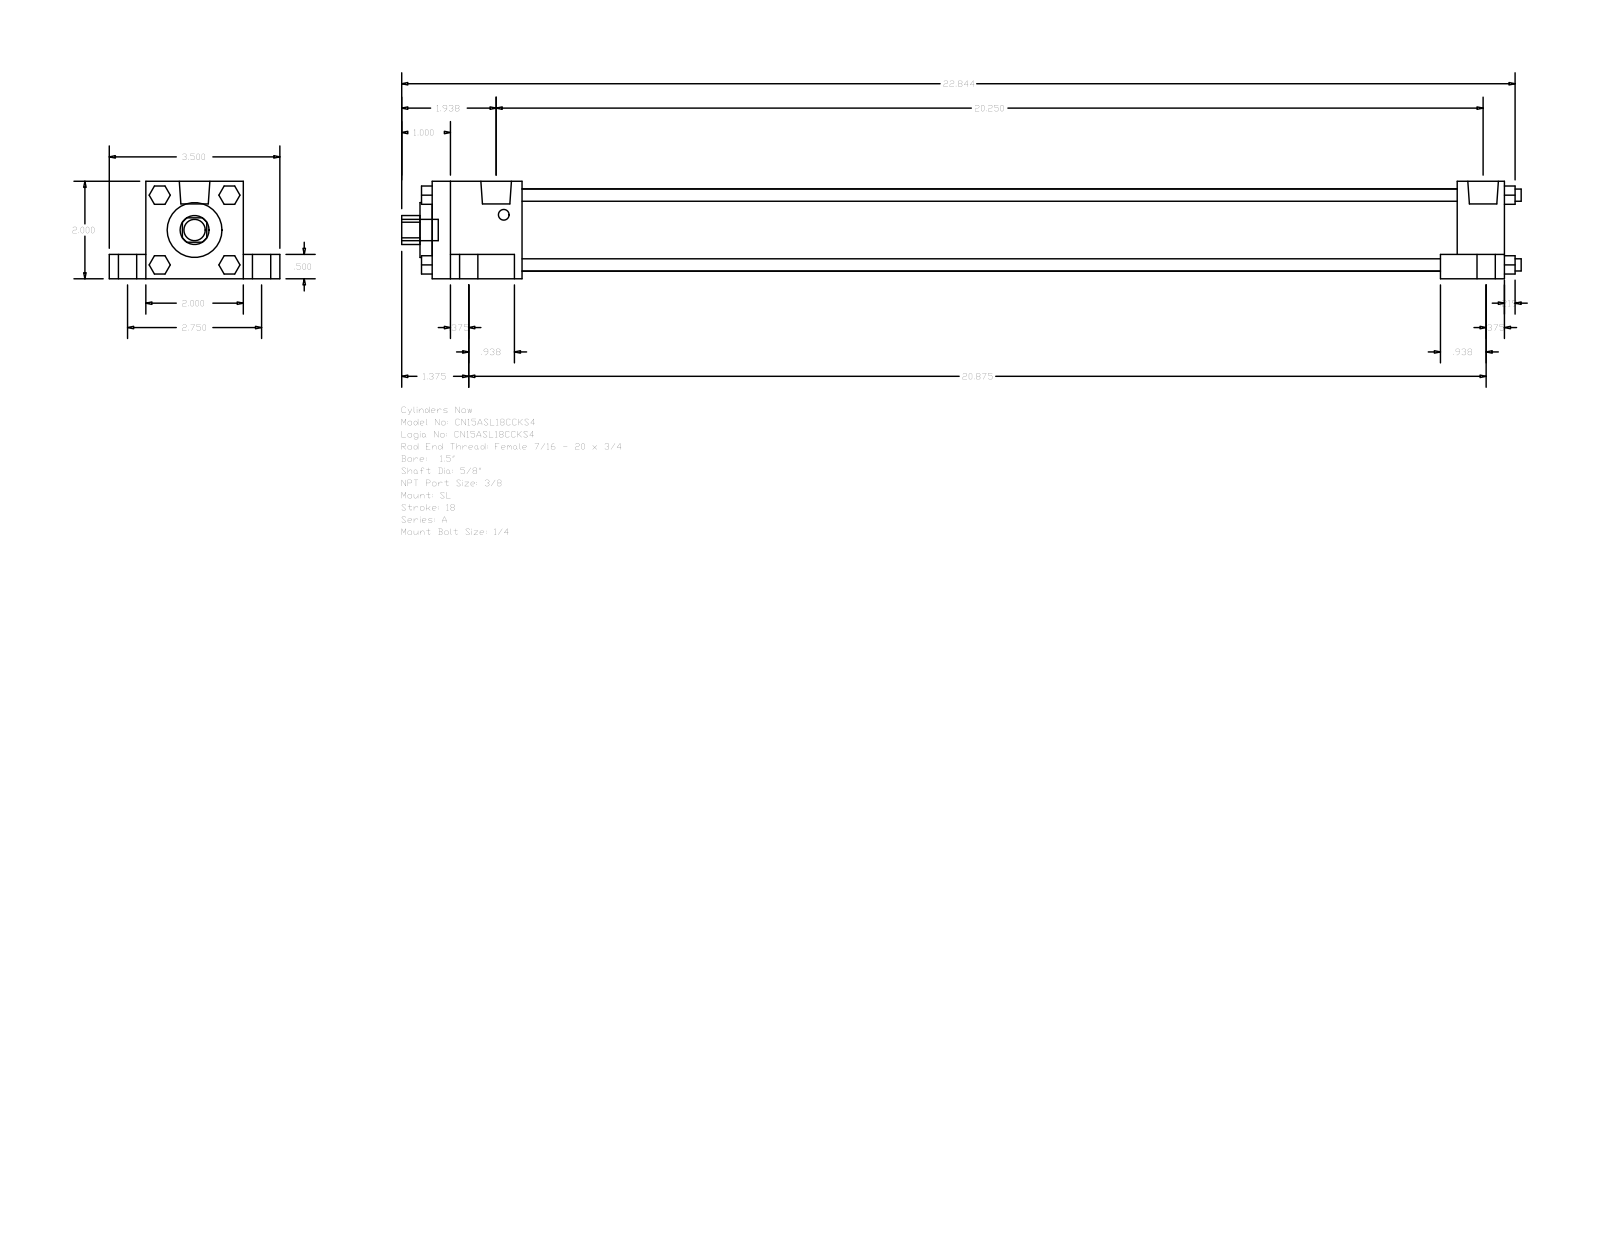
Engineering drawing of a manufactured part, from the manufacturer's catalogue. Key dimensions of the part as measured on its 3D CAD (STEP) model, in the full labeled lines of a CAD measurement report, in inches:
Part name (STEP PRODUCT): A_SL__0150_0.625
STEP written by: GSSL Pune (CONFIG_CONTROL_DESIGN)
Units: inches
Bodies: 0 solids, 148 faces (112 planar, 36 cylindrical, 0 other)
Overall size (bounding box): 22.969 × 3.5 × 2
Round holes (diameter × count): ⌀0.625 ×1, ⌀1.125 ×1, ⌀1.69 ×1
Round bosses / shafts (diameter × count): ⌀0.625 ×4, ⌀0.375 ×4, ⌀0.25 ×4, ⌀0.219 ×4, ⌀0.627 ×2, ⌀0.437 ×1
Partial cylindrical surfaces — rounded edges, fillets, slot ends (radius × count): R0.297 ×1
Main face-to-face distances: 2, 0.75, 0.5, 1.5, 2.75, 22, 0.375, 21.031, 0.969, 1.844
